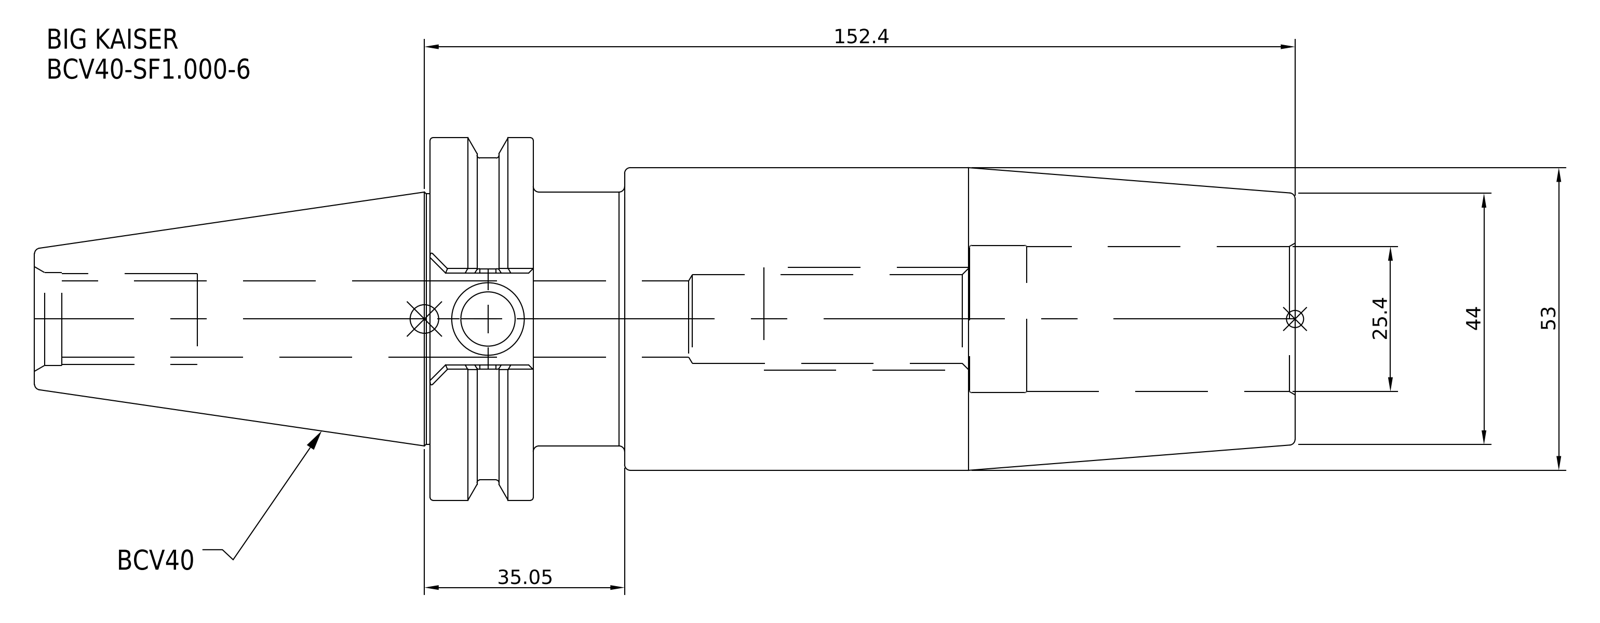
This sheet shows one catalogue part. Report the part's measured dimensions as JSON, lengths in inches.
{"part_name": "BCV40-SF1_000-6", "step_written_by": "SolidWorks 2021 (CONFIG_CONTROL_DESIGN)", "units": "inches", "bodies": {"solids": 1, "faces": 30, "planar": 8, "cylindrical": 14, "other": 8}, "overall_size": [8.687, 2.5, 2.5], "volume_in3": 22, "surface_area_in2": 66.06, "round_holes": [[1, 1]], "round_bosses_or_shafts": [[2.5, 1], [2.219, 1], [2.087, 1], [1.75, 1]], "face_to_face_distances": [0.711, 5.25, 5.961, 4.62, 0.63, 1.341, 1.85, 2.77, 3.4, 4.11]}
